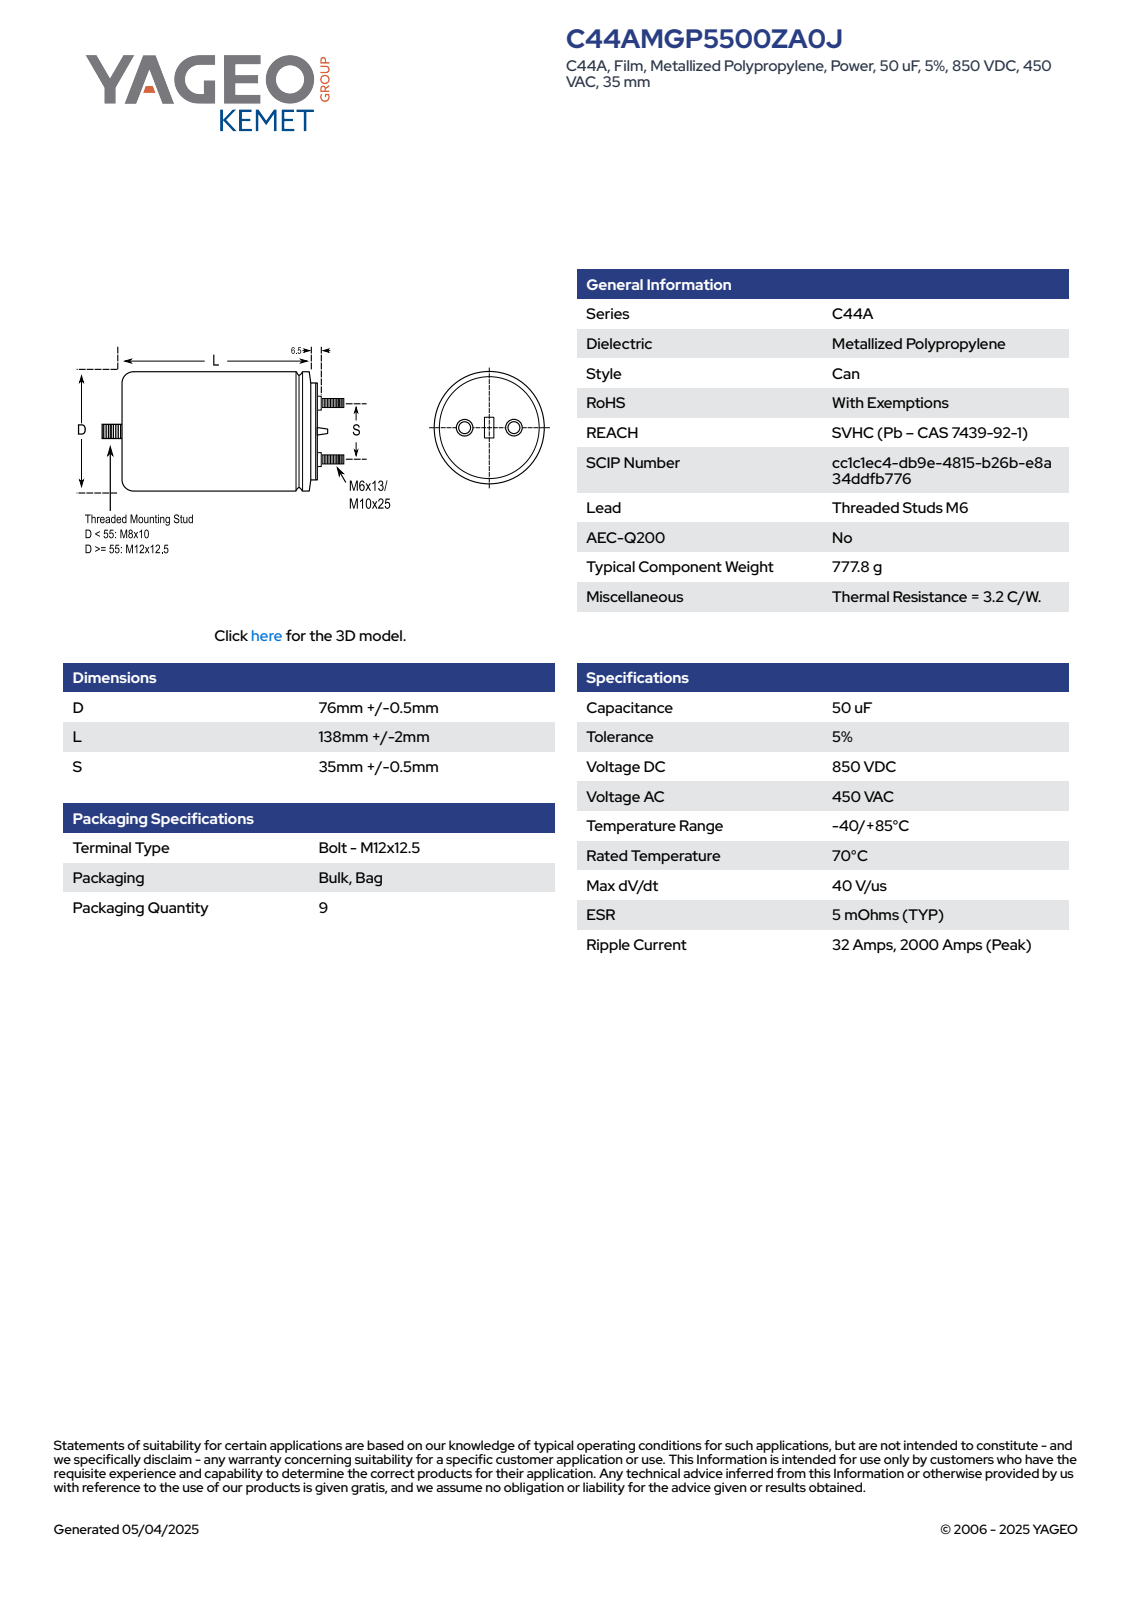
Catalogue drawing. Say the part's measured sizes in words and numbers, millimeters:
The part is named "CFP_C44A_76X138_D76.5L140S35". Its 3-D file was written by "SolidWorks 2014 (AUTOMOTIVE_DESIGN)". It is 1 solid with 102 faces: 29 planar, 34 cylindrical and 39 other. Overall it measures 172 by 76.5 by 76.5 millimeters. Its volume is 654 954 cubic millimeters and its surface area 44 474 square millimeters. Round bosses or shafts: 2 of diameter 9, 2 of diameter 6, 1 of diameter 76.5, 1 of diameter 60, 1 of diameter 12. Partial cylindrical surfaces (rounded edges, fillets, slot ends): 1 of radius 38.24. The main face-to-face distances are 145, 12.5, 157.5, 159, 146.5, 1.5, 172, 159.5, 14.5, 13.
